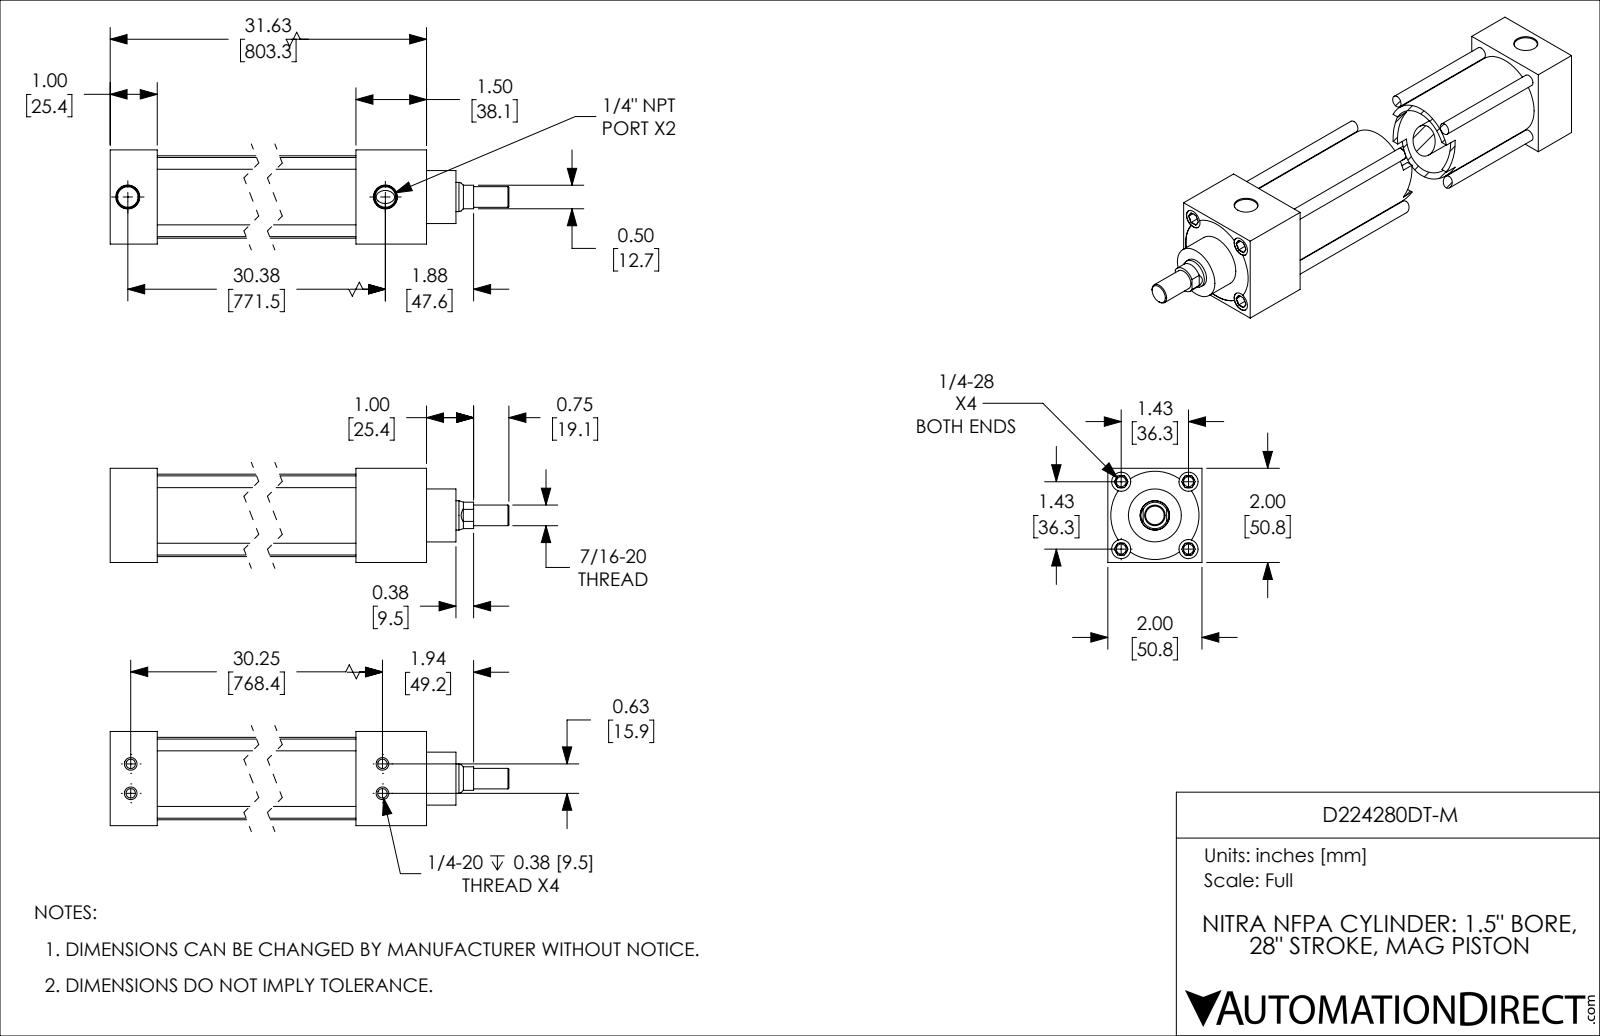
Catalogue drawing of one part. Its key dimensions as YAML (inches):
part_name: "D224280DT-M_BODY; D224280DT-M_PISTON_KK1; D224280DT-M"
step_written_by: "SolidWorks 2019 (CONFIG_CONTROL_DESIGN)"
units: inches
bodies: {solids: 2, faces: 203, planar: 58, cylindrical: 65, other: 80}
overall_size: [33.375, 2, 2]
volume: 45.12
surface_area: 506.2
round_holes:
  - {diameter: 0.201, count: 4}
  - {diameter: 0.213, count: 4}
  - {diameter: 0.406, count: 4}
  - {diameter: 0.438, count: 2}
  - {diameter: 0.626, count: 1}
  - {diameter: 1.501, count: 1}
round_bosses_or_shafts:
  - {diameter: 0.25, count: 4}
  - {diameter: 1.751, count: 1}
  - {diameter: 1.499, count: 1}
  - {diameter: 1.125, count: 1}
  - {diameter: 0.624, count: 1}
  - {diameter: 0.437, count: 1}
partial_cylinders:
  - {radius: 0.281, count: 1}
  - {radius: 0.937, count: 1}
face_to_face_distances: [2, 1, 30.125, 29.125, 31.62, 30.62, 1.495, 1.125, 2.125, 28]
hole_center_spacings: [0.319, 1.011, 1.43, 0.625, 2.022, 30.25, 30.256, 30.314]
